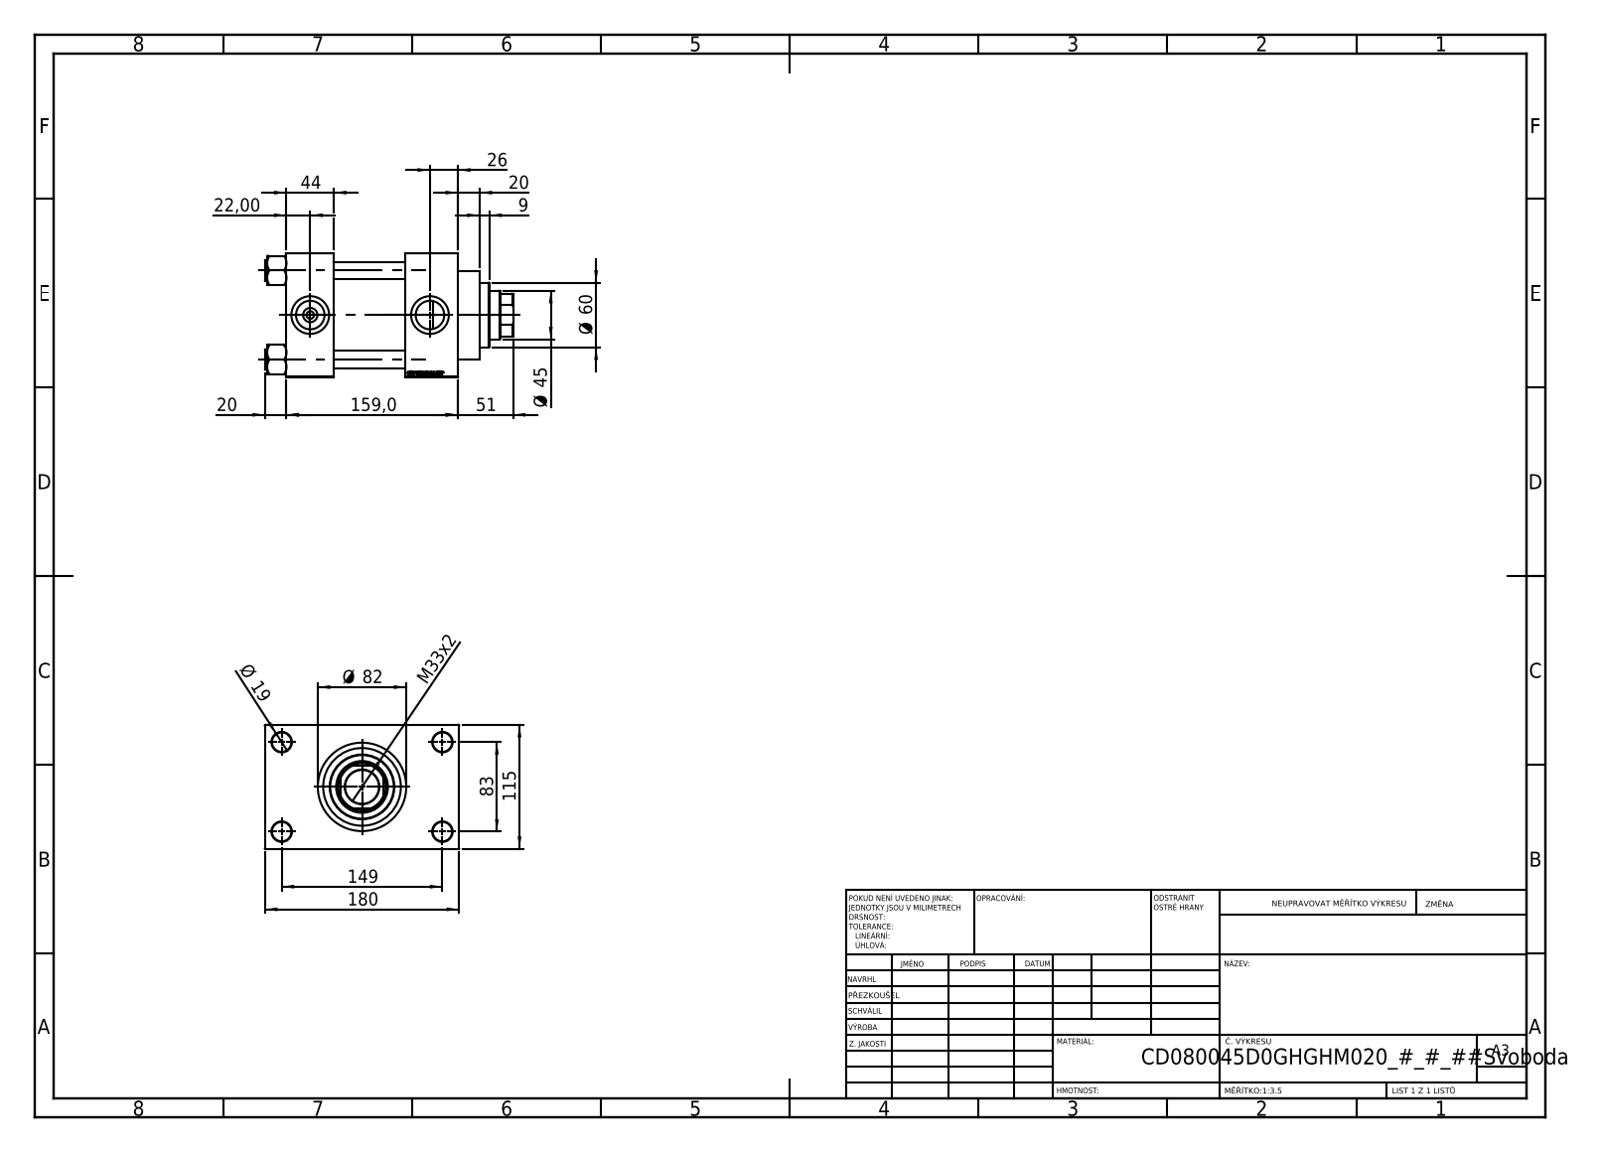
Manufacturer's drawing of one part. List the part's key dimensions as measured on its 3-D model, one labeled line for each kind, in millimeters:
Part name (STEP PRODUCT): V215CD_NUT_M5_D; V215CD_D_Body; V215CD_D_TYCINKA; V215CD_VCP_D (+1 more)
STEP written by: SolidWorks 2019 (CONFIG_CONTROL_DESIGN)
Units: millimetres
Bodies: 11 solids, 1151 faces (545 planar, 88 cylindrical, 518 other)
Overall size (bounding box): 230 × 180 × 115
Volume: 2 004 000 mm³ · Surface area: 302 449 mm²
Round holes (diameter × count): ⌀16 ×4, ⌀18 ×4, ⌀7 ×2, ⌀26.44 ×2, ⌀35 ×2, ⌀31.5 ×1, ⌀45 ×1, ⌀48 ×1, ⌀61 ×1, ⌀72 ×1, ⌀80 ×1
Round bosses / shafts (diameter × count): ⌀19 ×4, ⌀86 ×1, ⌀82 ×1, ⌀60 ×1
Partial cylindrical surfaces — rounded edges, fillets, slot ends (radius × count): R22 ×1
Main face-to-face distances: 115, 110, 66, 49, 44, 159, 32.5, 147.5, 20, 69
Hole centre spacings: 33.15, 58.48, 82.7, 85.28, 89.24, 115.85, 142.43, 83
